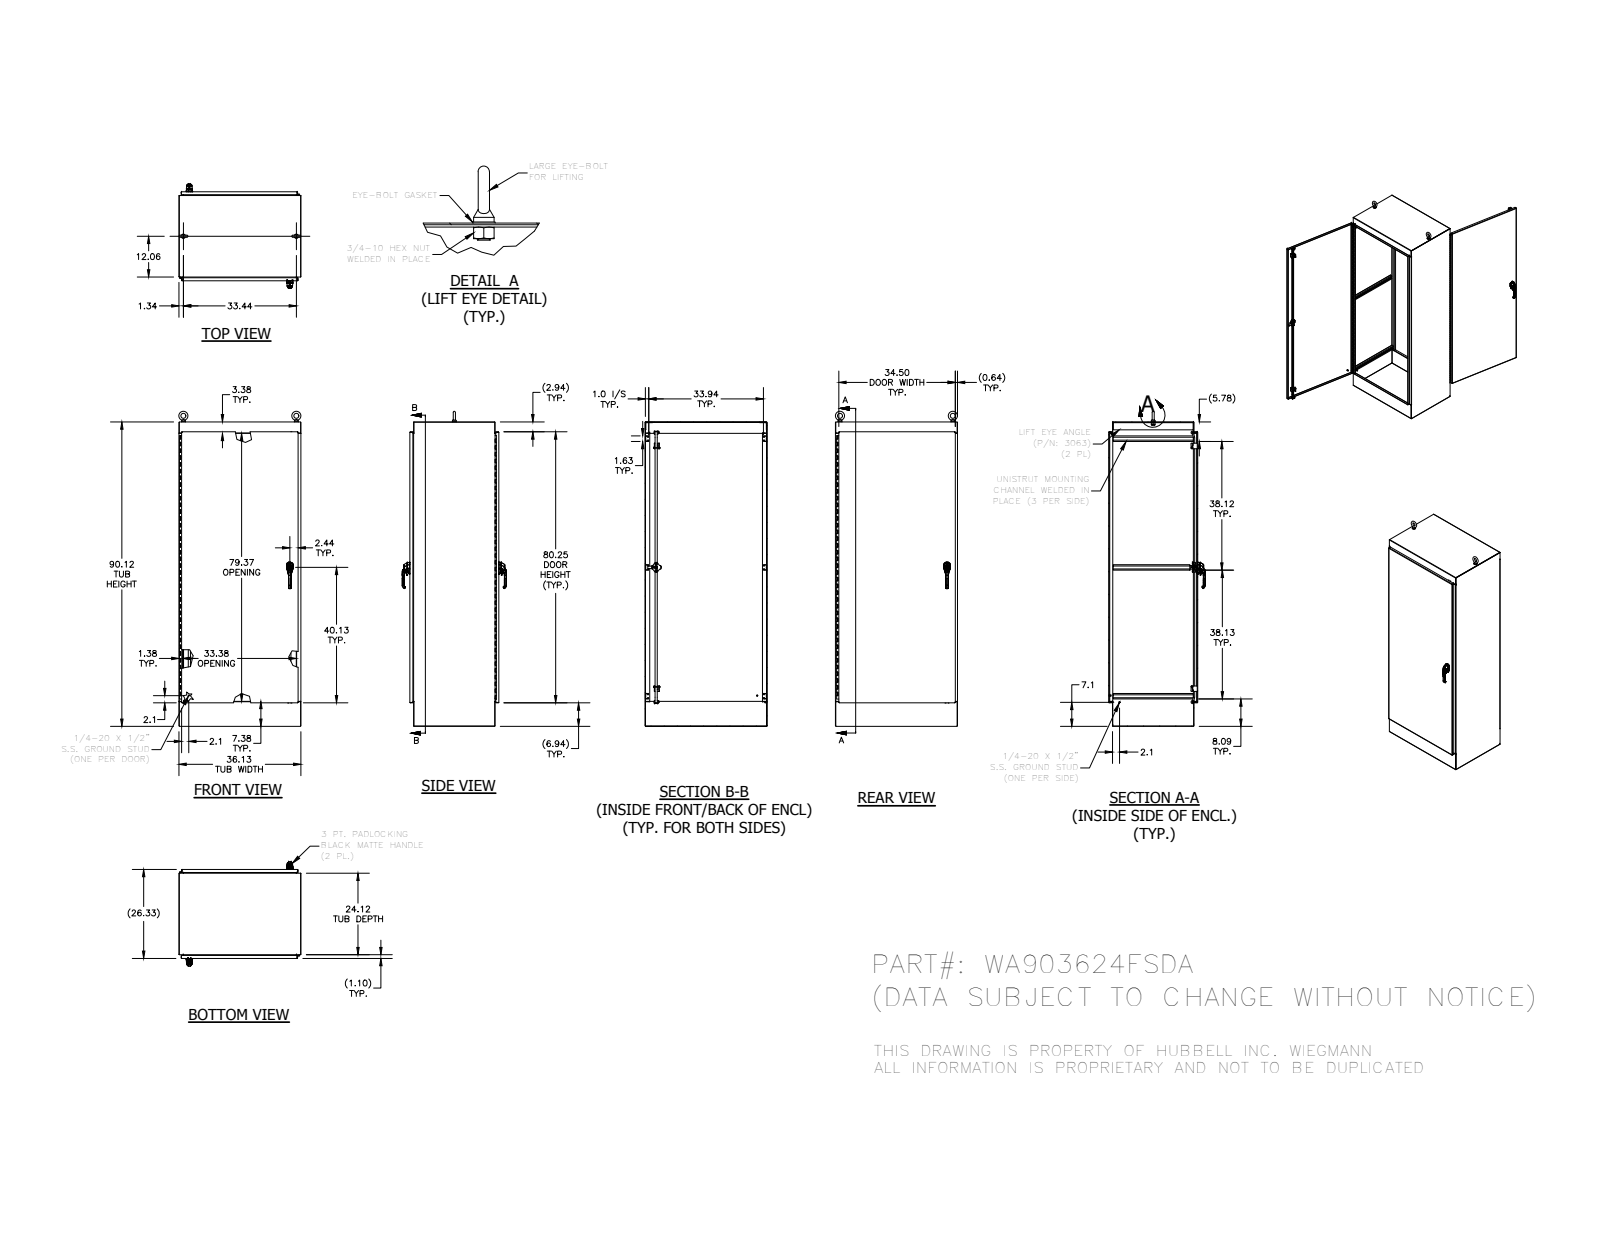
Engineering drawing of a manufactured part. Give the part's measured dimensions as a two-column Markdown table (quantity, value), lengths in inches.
| quantity | value |
| --- | --- |
| part name | WA9024FSDALRS; WA3624FSDABTM; WA3624FSDATOP; WA9036FSDADR (+8 more) |
| STEP written by | Autodesk Inventor 2014 (AUTOMOTIVE_DESIGN) |
| units | inches |
| bodies | 84 solids, 5600 faces (2358 planar, 1978 cylindrical, 1264 other) |
| overall size | 93.248 × 36.125 × 30.871 |
| volume | 1 584 in³ |
| surface area | 30 400 in² |
| round holes (diameter × count) | 0.276 × 16, 0.375 × 16, 0.2 × 8, 0.213 × 6, 0.236 × 6, 0.28 × 6, 0.241 × 4, 0.25 × 4, 0.252 × 4, 0.4 × 4, 0.407 × 4, 0.413 × 4 |
| round bosses / shafts (diameter × count) | 1 × 4, 0.563 × 4, 0.526 × 4, 0.5 × 4, 0.375 × 4, 0.337 × 4, 0.313 × 4, 0.281 × 4 |
| partial cylindrical surfaces (radius × count) | 0.02 × 333, 0.012 × 174, 0.019 × 38, 0.01 × 32, 0.079 × 30, 0.05 × 28, 0.031 × 26, 0.118 × 24 |
| main face-to-face distances | 0.094, 0.125, 26.209, 36.031, 26.084, 26.334, 35.938, 36.125, 90.031, 1.104 |
| hole center spacings | 35.33, 38.386, 26, 43.001, 8.667, 17.333, 34.25, 8.667 |
